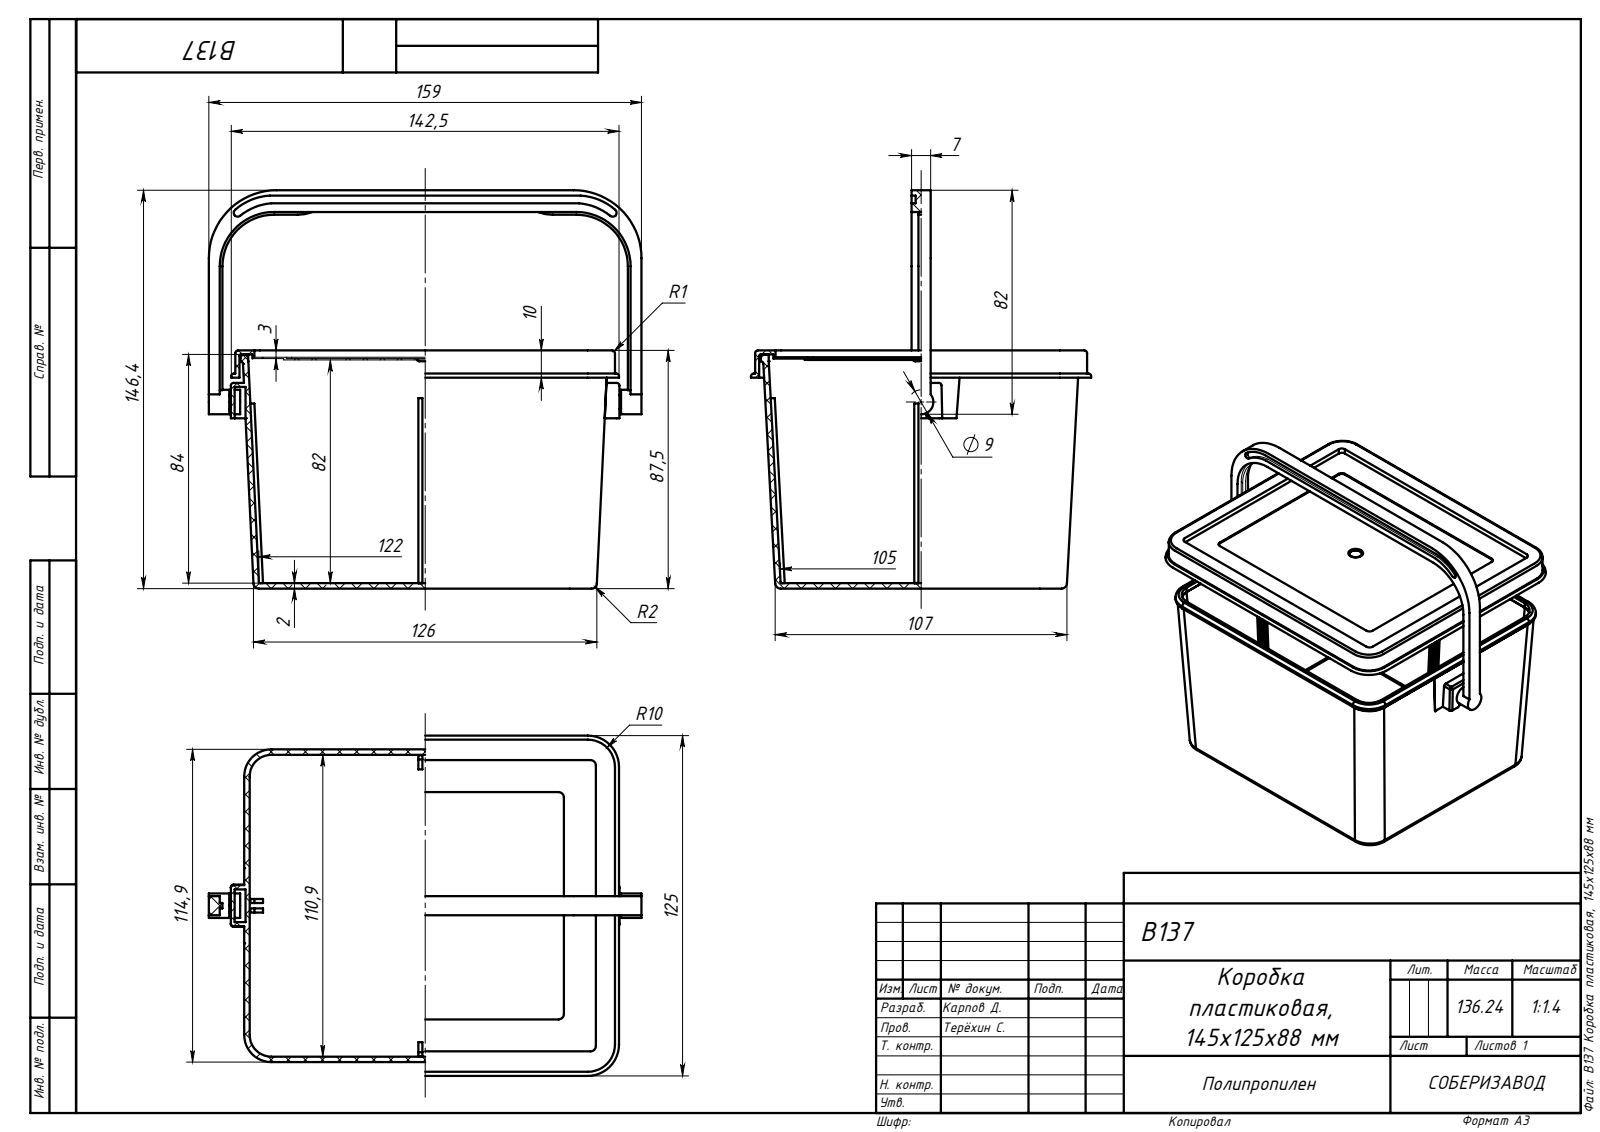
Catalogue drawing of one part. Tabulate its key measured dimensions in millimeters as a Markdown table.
| quantity | value |
| --- | --- |
| part name | B137 Емкость; B137 Ручка; B137 Крышка; B137 Коробка пластиковая, 145x125x88 мм |
| STEP written by | SolidWorks 2020 (AUTOMOTIVE_DESIGN) |
| units | millimeters |
| bodies | 4 solids, 352 faces (170 planar, 122 cylindrical, 60 other) |
| overall size | 159 × 146.35 × 125 |
| volume | 139 309 mm³ |
| surface area | 163 874 mm² |
| round bosses / shafts (diameter × count) | 9 × 1, 5 × 1 |
| partial cylindrical surfaces (radius × count) | 1 × 22, 2 × 12, 0.5 × 8, 1.5 × 8, 3 × 8, 10 × 8, 8 × 4, 8.5 × 4 |
| main face-to-face distances | 2, 0.5, 84.5, 82.5, 1.5, 84, 82, 1, 3.5, 85 |
